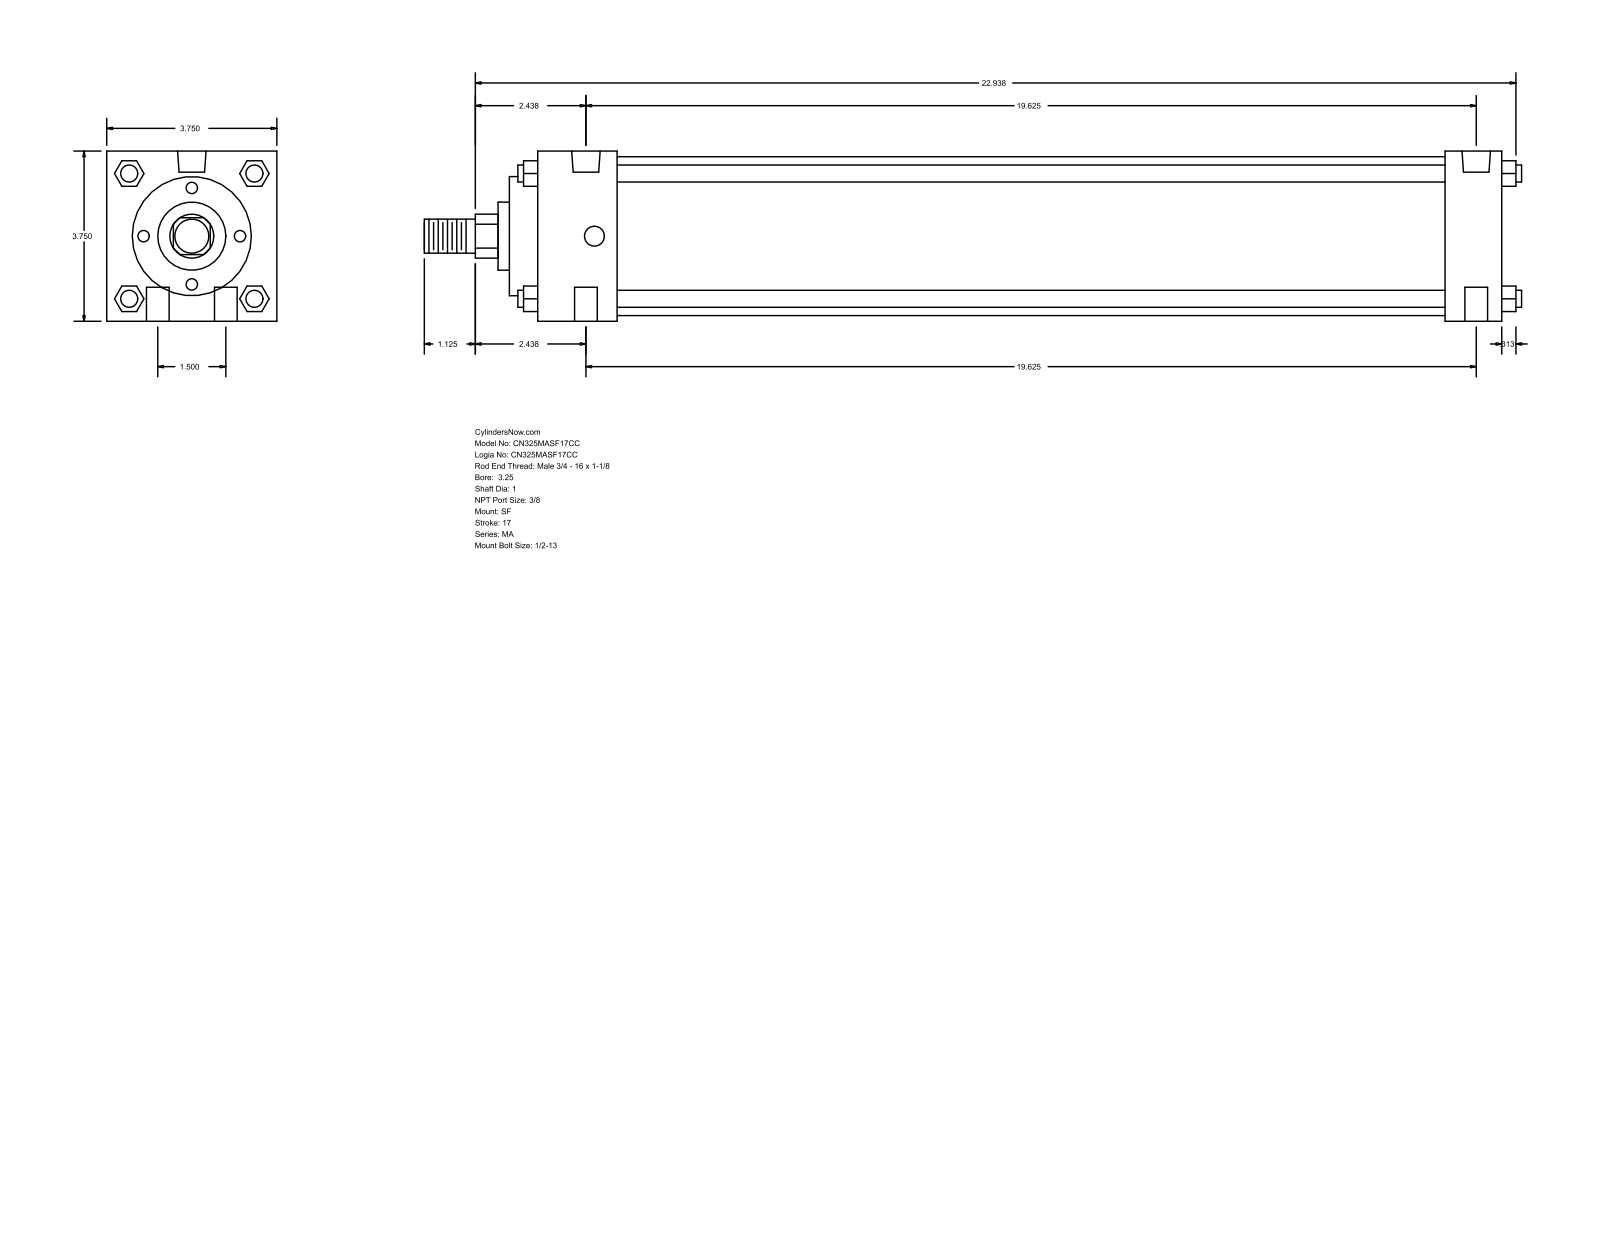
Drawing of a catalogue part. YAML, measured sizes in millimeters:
part_name: "MA_SF__0325_1"
step_written_by: "GSSL Pune (CONFIG_CONTROL_DESIGN)"
units: millimeters
bodies: {solids: 0, faces: 126, planar: 95, cylindrical: 31, other: 0}
overall_size: [614.36, 95.25, 95.25]
round_holes:
  - {diameter: 12.7, count: 4}
  - {diameter: 11.11, count: 2}
  - {diameter: 15.93, count: 2}
round_bosses_or_shafts:
  - {diameter: 9.53, count: 4}
  - {diameter: 88.9, count: 1}
  - {diameter: 66.67, count: 1}
  - {diameter: 38.1, count: 1}
  - {diameter: 25.4, count: 1}
  - {diameter: 19.05, count: 1}
partial_cylinders:
  - {radius: 12.29, count: 1}
face_to_face_distances: [95.24, 539.75, 555.62, 508, 31.75, 44.46, 463.54, 495.29, 15.87, 60.33]
hole_center_spacings: [19.05, 498.84, 498.48, 38.1, 499.93, 488.95]
